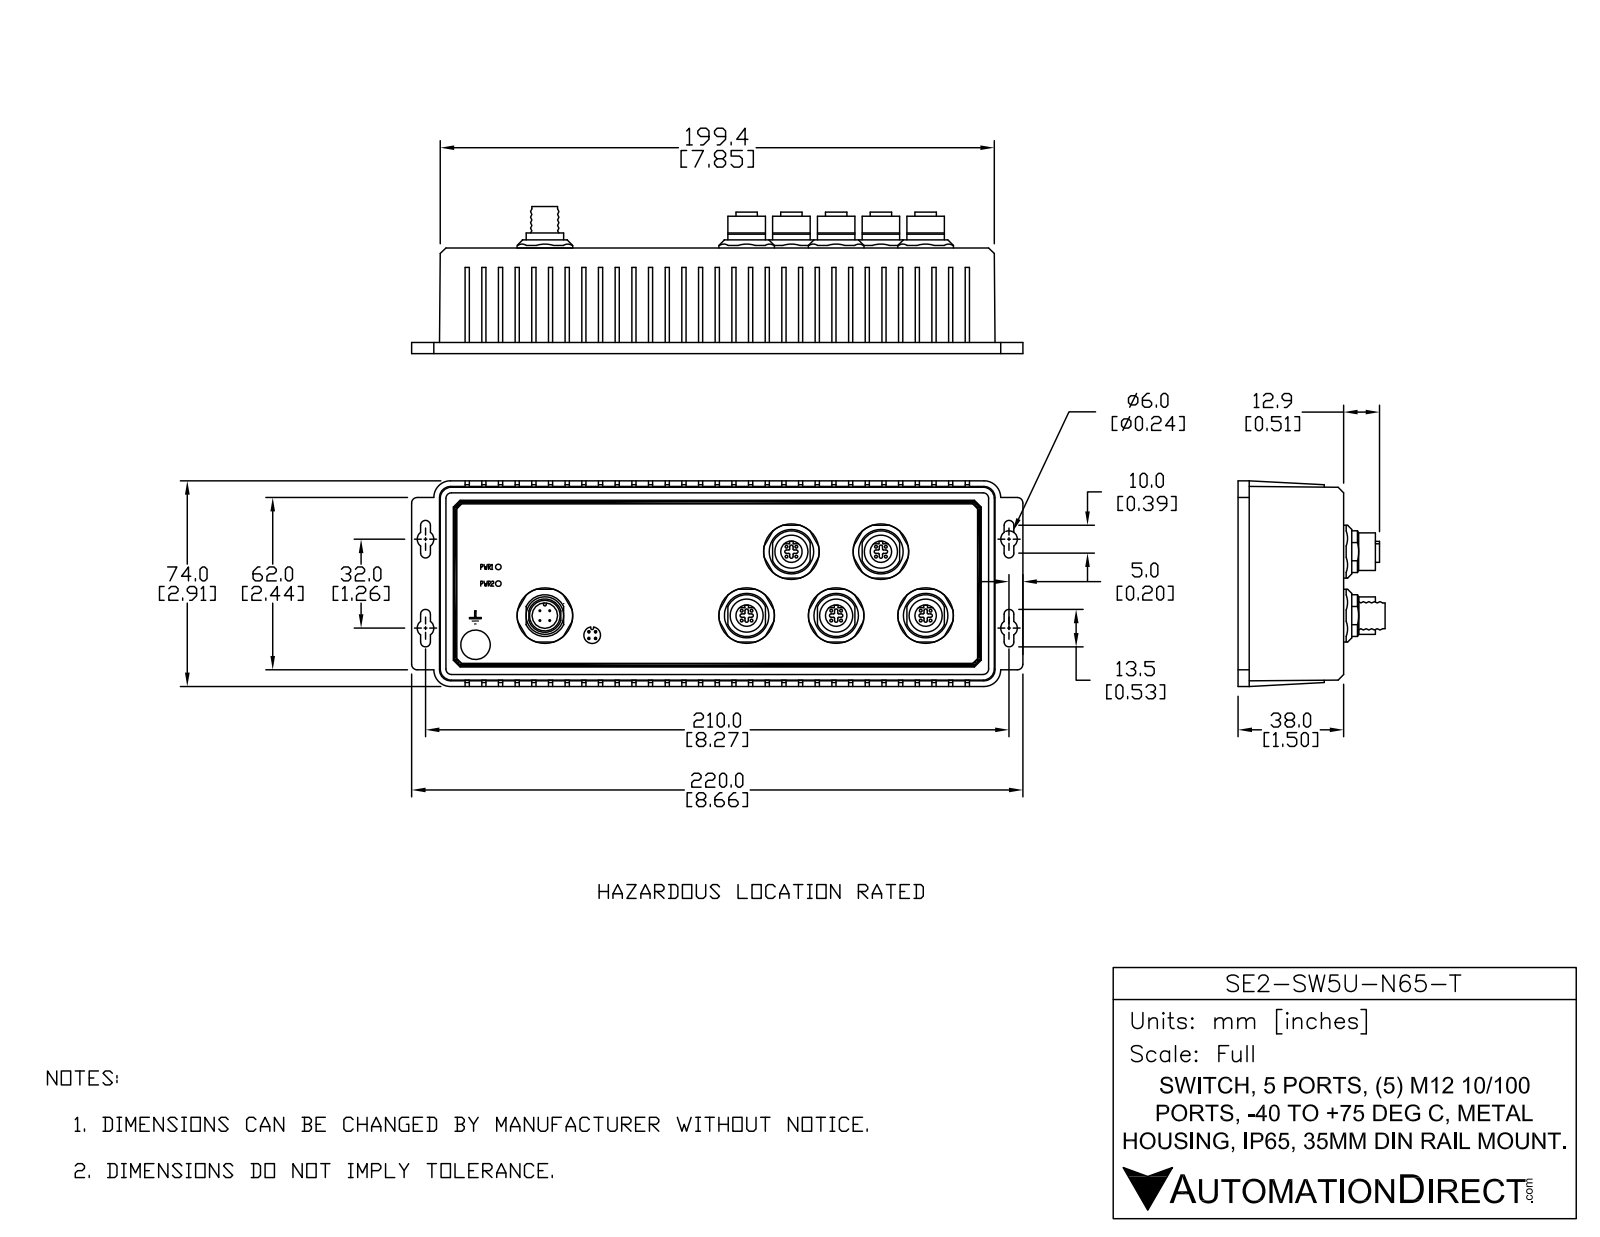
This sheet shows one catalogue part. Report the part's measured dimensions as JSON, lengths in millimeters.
{"part_name": "SE2-SW5U-N65-T", "step_written_by": "SolidWorks 2017 (AUTOMOTIVE_DESIGN)", "units": "millimeters", "bodies": {"solids": 16, "faces": 1208, "planar": 718, "cylindrical": 329, "other": 161}, "overall_size": [222.4, 78.4, 51.8], "volume_mm3": 168600, "surface_area_mm2": 127000, "round_holes": [[1, 20], [3, 18], [17.5, 8], [14.7, 6], [11.1, 5], [3.8, 1], [5, 1], [9.5, 1], [21, 1]], "round_bosses_or_shafts": [[12.7, 6], [22.7, 5], [15.9, 5], [0.8, 4], [15.9, 1], [8, 1], [3.5, 1]], "partial_cylinders_radius": [[0.3, 50], [3, 34], [2, 32], [0.5, 28], [1.8, 8], [2.7, 8], [3.3, 8], [4.2, 8]], "face_to_face_distances": [1.5, 3.5, 0.5, 35.3, 32.3, 3, 33.8, 36.8, 1, 35.8], "hole_center_spacings": [2.2, 28.1, 3.1, 4.4, 32.2, 2.2, 3.1, 30.3]}
